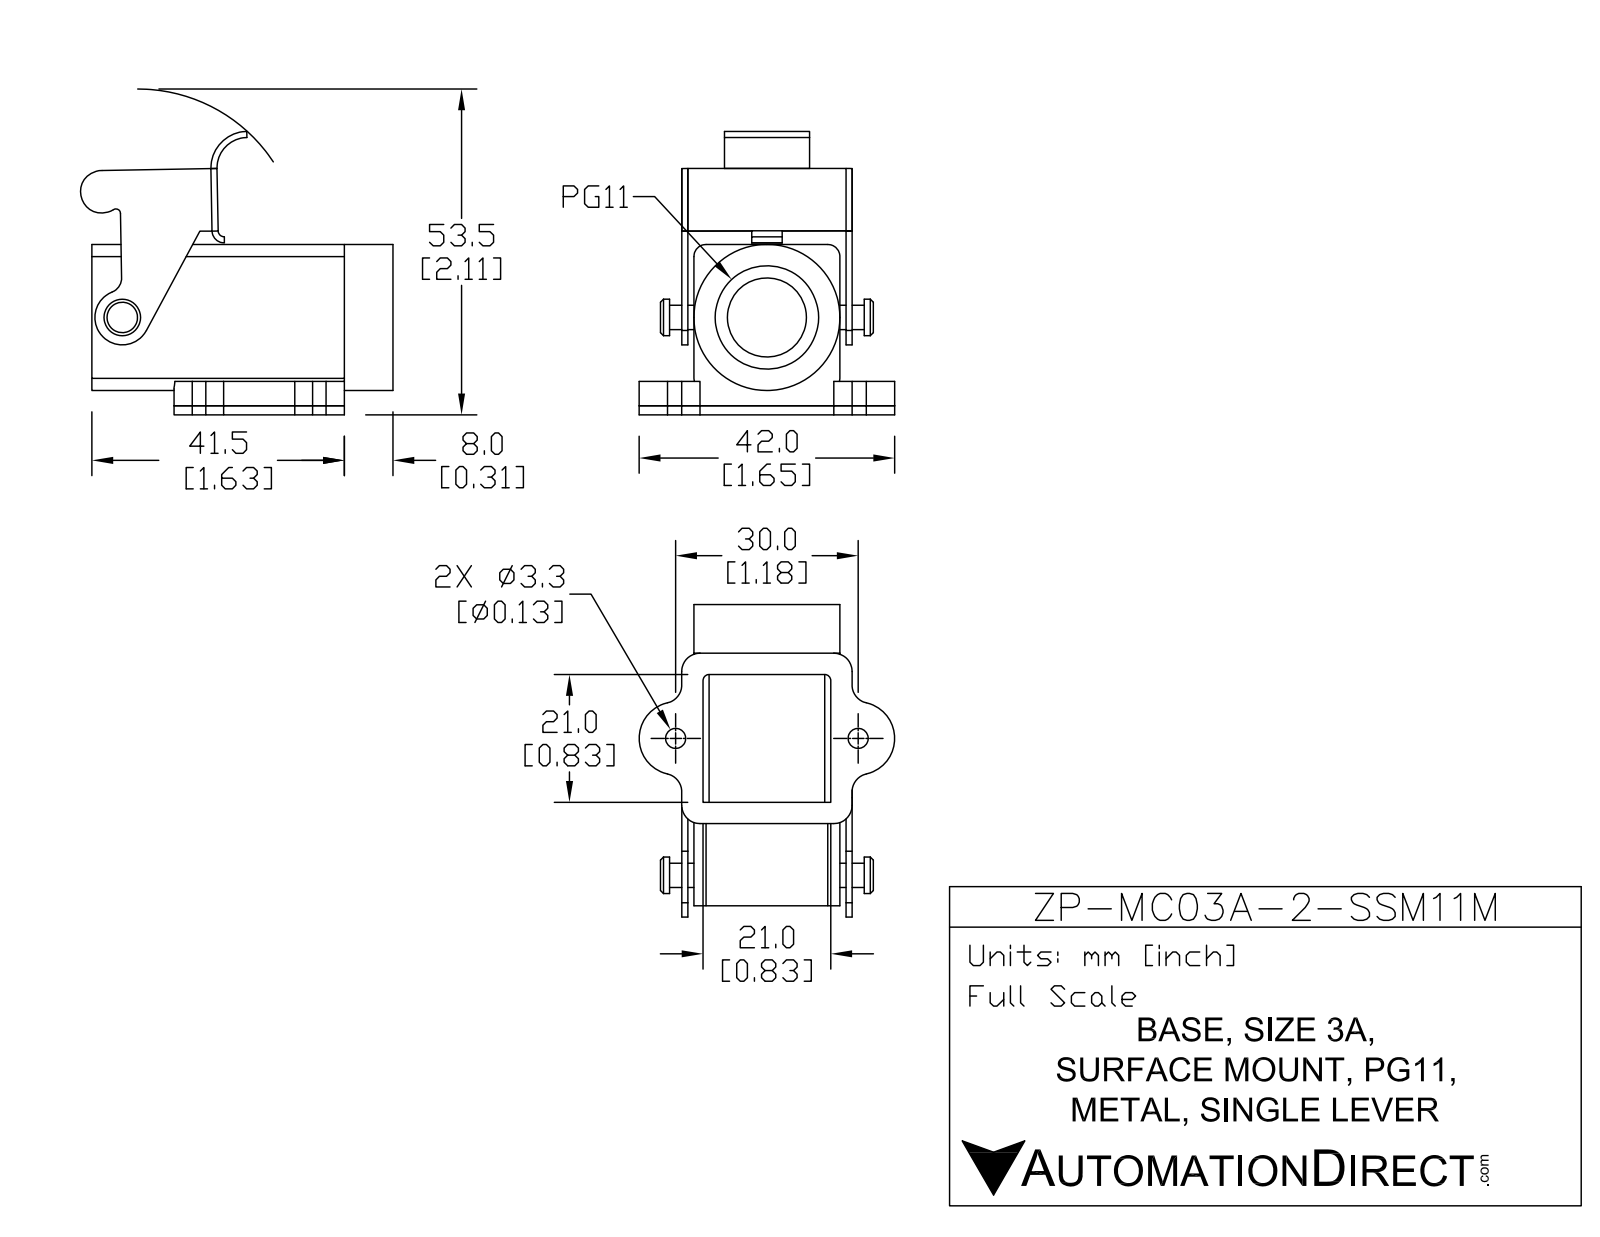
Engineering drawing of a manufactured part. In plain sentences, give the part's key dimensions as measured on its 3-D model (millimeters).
The part is named "ZP-MC03A-2-SSM11M". Its 3-D file was written by "SolidWorks 2011 (AUTOMOTIVE_DESIGN)". It is 2 solids with 142 faces: 65 planar, 72 cylindrical and 5 other. Overall it measures 56.44 by 53.37 by 42 millimeters. Its volume is 11 172 cubic millimeters and its surface area 13 436 square millimeters. Round holes: 2 of diameter 3.3, 1 of diameter 3, 1 of diameter 13, 1 of diameter 17. Round bosses or shafts: 1 of diameter 24, 1 of diameter 6, 1 of diameter 4. Partial cylindrical surfaces (rounded edges, fillets, slot ends): 10 of radius 2, 8 of radius 3, 6 of radius 1, 4 of radius 0.5, 2 of radius 6, 1 of radius 1, 1 of radius 3.45, 1 of radius 3.73. The main face-to-face distances are 1.5, 22.5, 21, 25, 26.5, 24, 2.5, 1.15, 4, 1. The hole center spacings are 22.3, 30.
